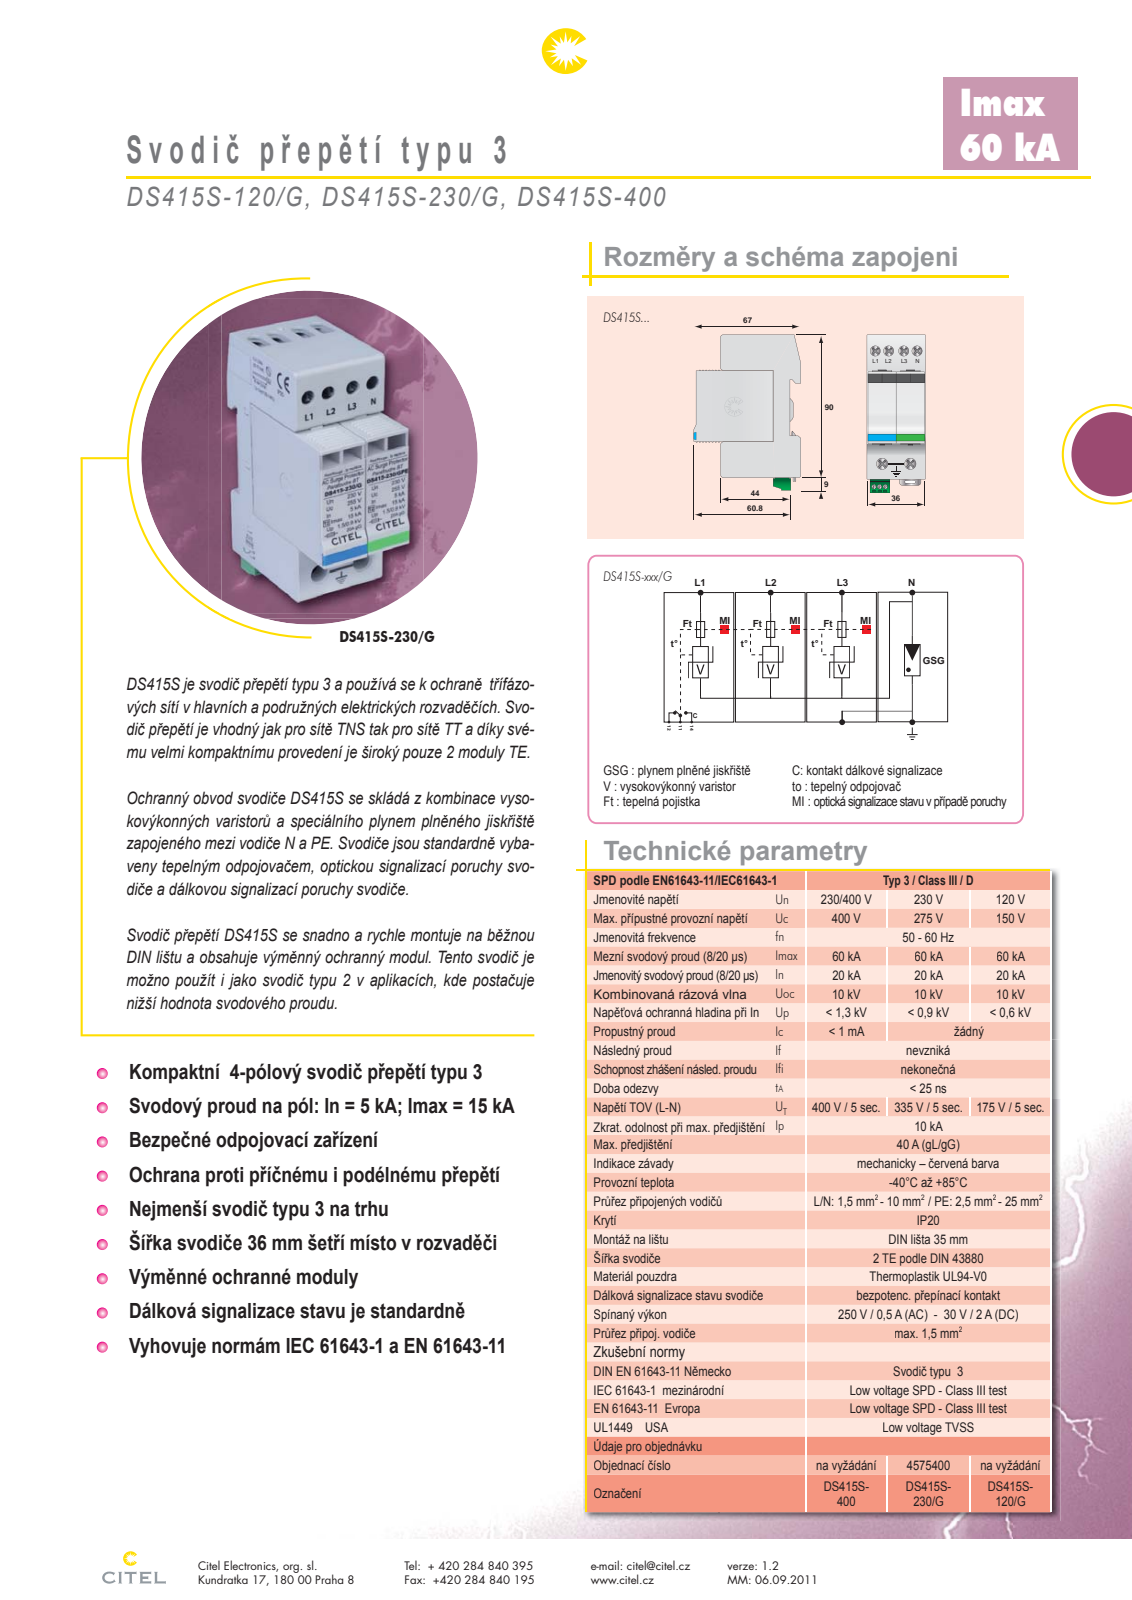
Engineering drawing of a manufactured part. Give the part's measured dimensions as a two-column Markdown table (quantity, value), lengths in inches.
| quantity | value |
| --- | --- |
| part name | DS415S |
| STEP written by | Creo Elements/Direct Modeling 20.0AP0401 12-May-2017 (C) Parametric Technology GmbH (AUTOMOTIVE_DESIGN) |
| units | inches |
| bodies | 1 solid, 935 faces (747 planar, 137 cylindrical, 51 other) |
| overall size | 3.856 × 2.654 × 1.417 |
| volume | 9.688 in³ |
| surface area | 80.25 in² |
| round holes (diameter × count) | 0.209 × 4, 0.11 × 3, 0.276 × 2 |
| round bosses / shafts (diameter × count) | 0.268 × 4, 0.394 × 2, 0.354 × 2, 0.197 × 2, 0.157 × 1 |
| partial cylindrical surfaces (radius × count) | 0.039 × 16, 0.098 × 9, 0.059 × 8, 0.118 × 8, 0.008 × 6, 0.012 × 4, 0.02 × 4, 0.071 × 4 |
| main face-to-face distances | 0.715, 0.689, 0.701, 0.703, 0.014, 1.404, 1.417, 2.648, 0.896, 1.39 |
| hole center spacings | 2.76, 0.701, 0.138, 0.315, 2.809, 2.887, 0.276, 0.386 |
